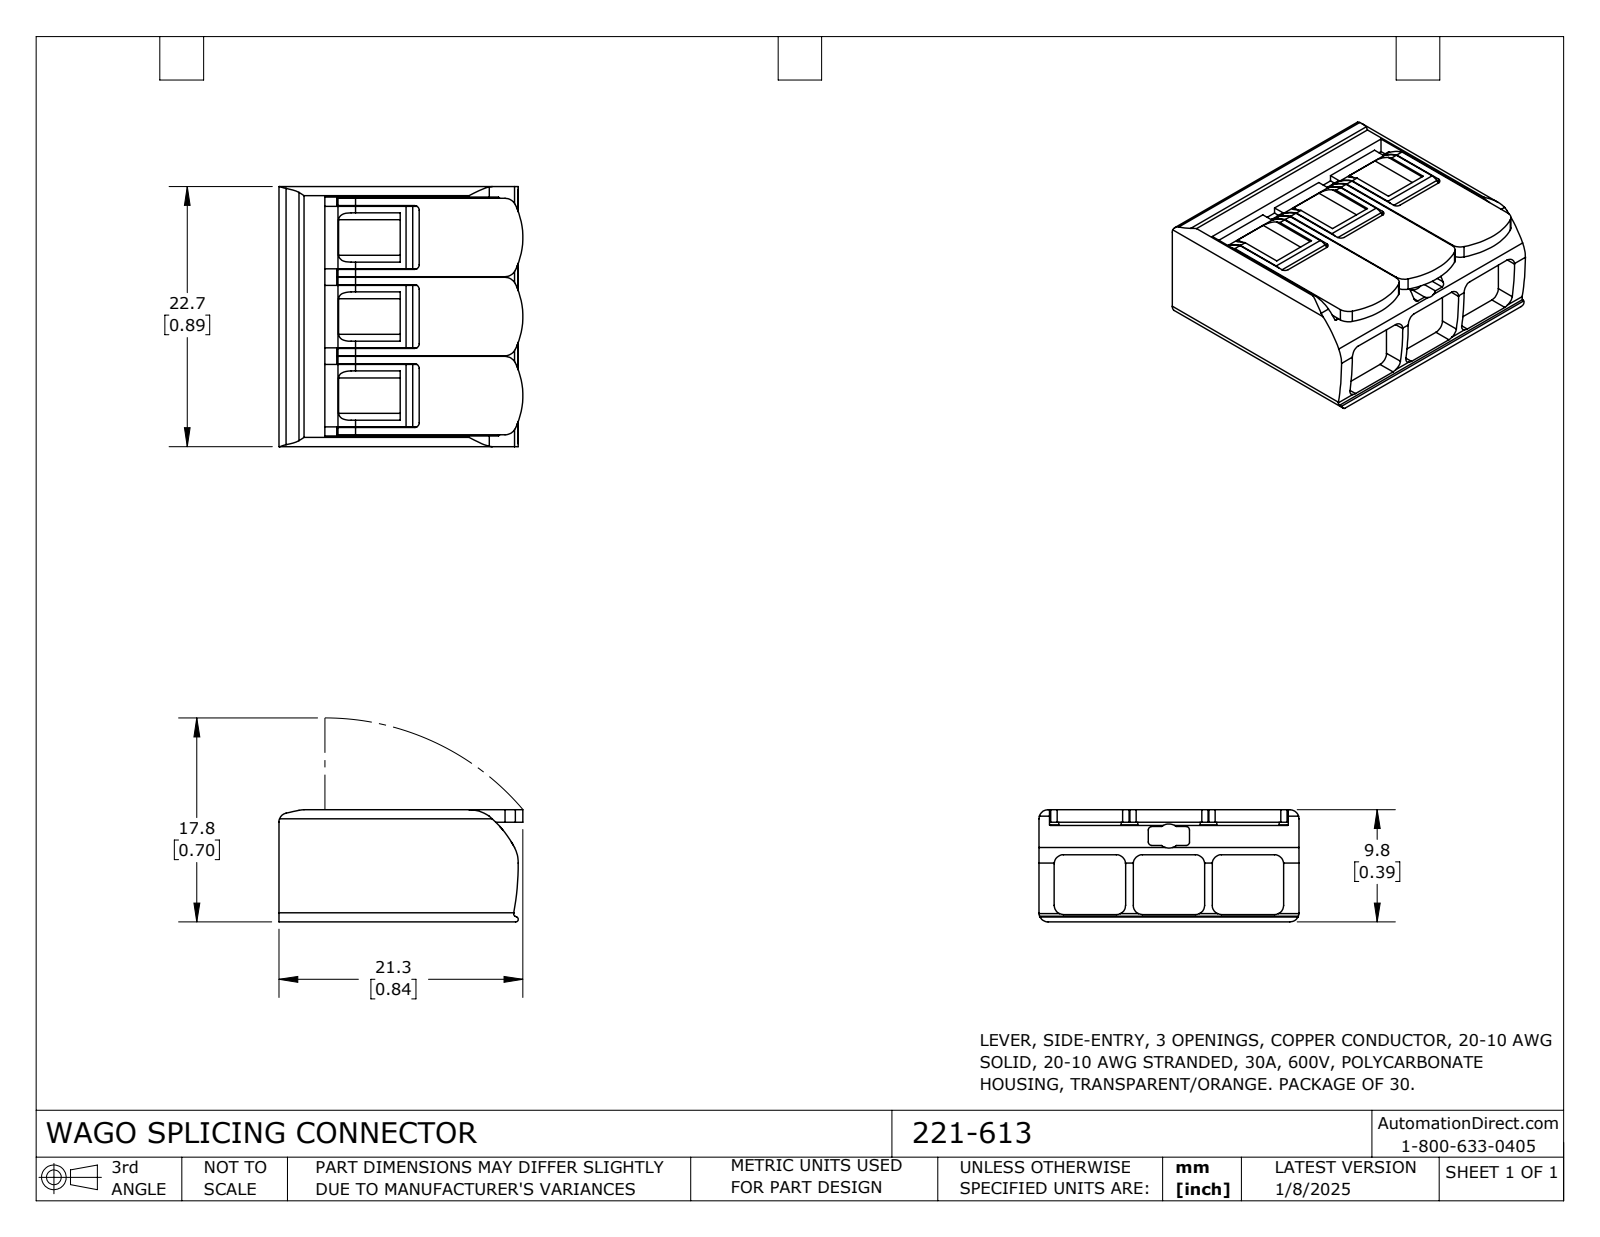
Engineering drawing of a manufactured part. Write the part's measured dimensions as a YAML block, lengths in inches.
part_name: "221-613"
step_written_by: "SolidWorks 2023 (CONFIG_CONTROL_DESIGN)"
units: inches
bodies: {solids: 1, faces: 167, planar: 98, cylindrical: 69, other: 0}
overall_size: [0.894, 0.839, 0.386]
volume: 0.26
surface_area: 3.632
partial_cylinders:
  - {radius: 0.031, count: 17}
  - {radius: 0.039, count: 7}
  - {radius: 0.016, count: 6}
  - {radius: 0.024, count: 6}
  - {radius: 0.012, count: 4}
  - {radius: 0.256, count: 3}
  - {radius: 0.008, count: 1}
  - {radius: 0.009, count: 1}
face_to_face_distances: [0.386, 0.894, 0.744, 0.343, 0.043, 0.272, 0.03, 0.333, 0.053, 0.356]
